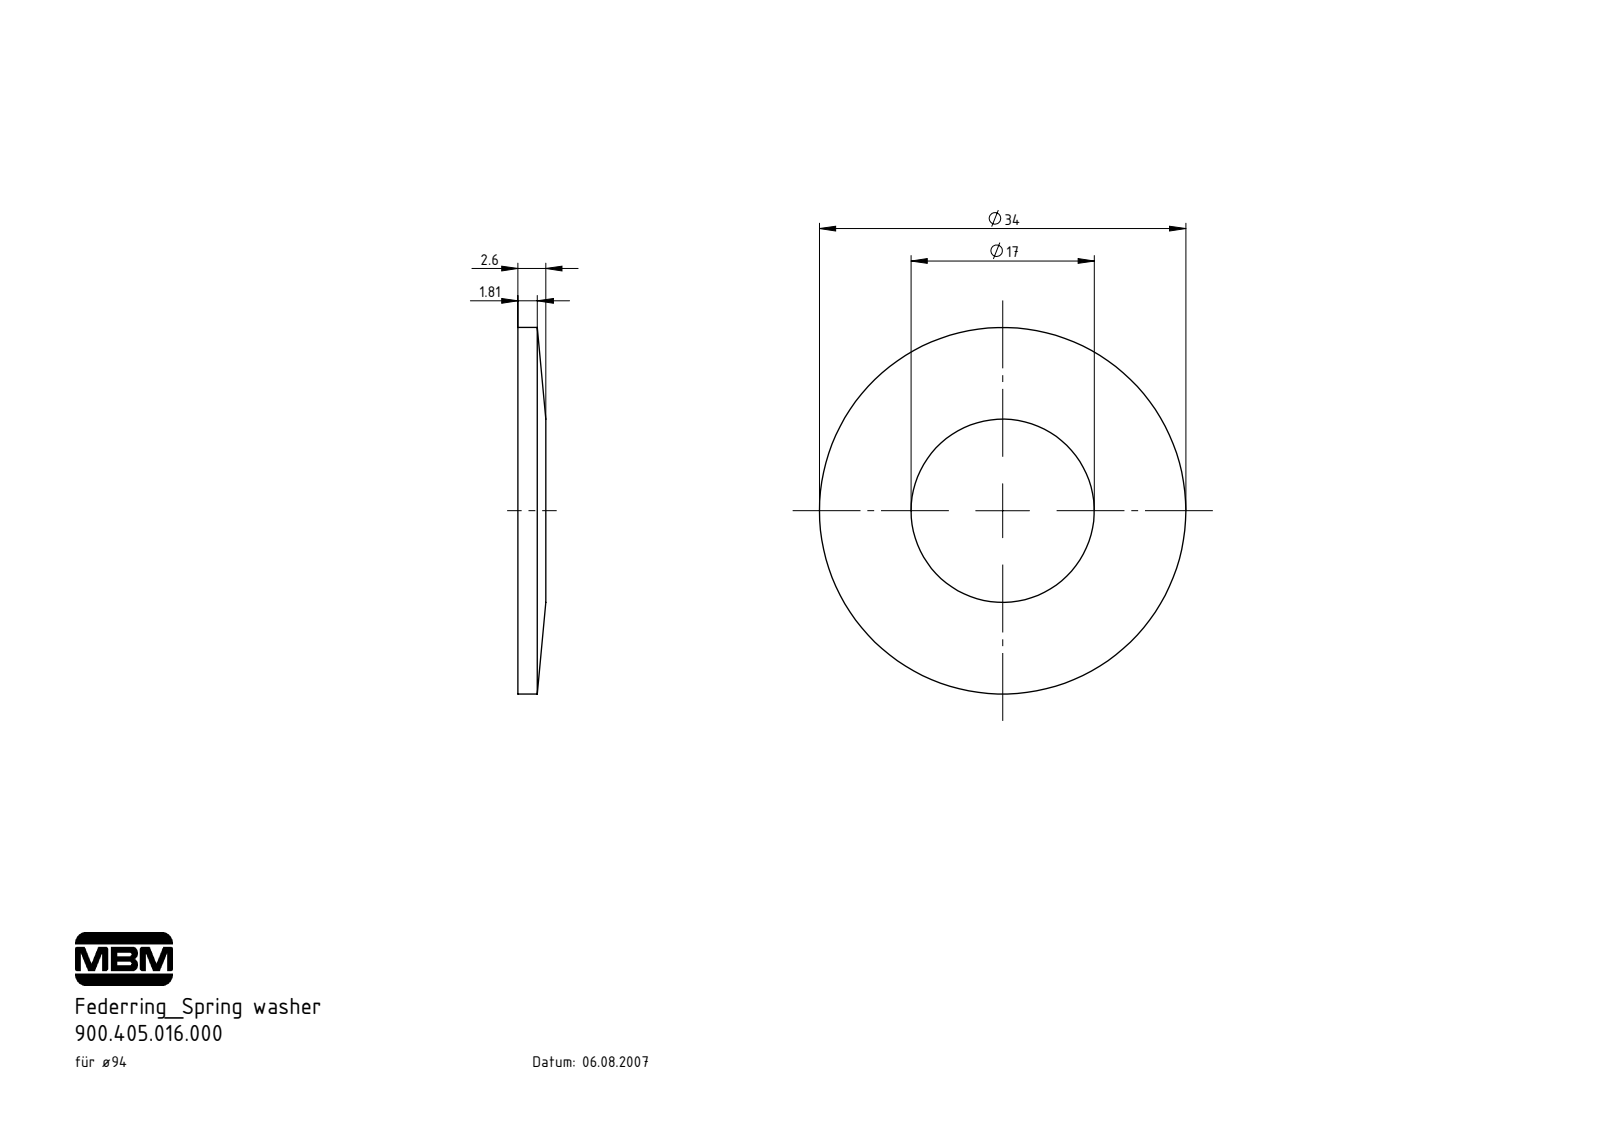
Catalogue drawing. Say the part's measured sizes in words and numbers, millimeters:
The part is named "900.405.016.000". Its 3-D file was written by "SolidWorks 2022 (AUTOMOTIVE_DESIGN)". It is 1 solid with 6 faces: 2 planar, 4 cylindrical and 0 other. Overall it measures 34 by 34 by 1.8 millimeters. Its volume is 1 226 cubic millimeters and its surface area 1 650 square millimeters. Round holes: 1 of diameter 17. Round bosses or shafts: 1 of diameter 34. The main face-to-face distances are 1.8.
